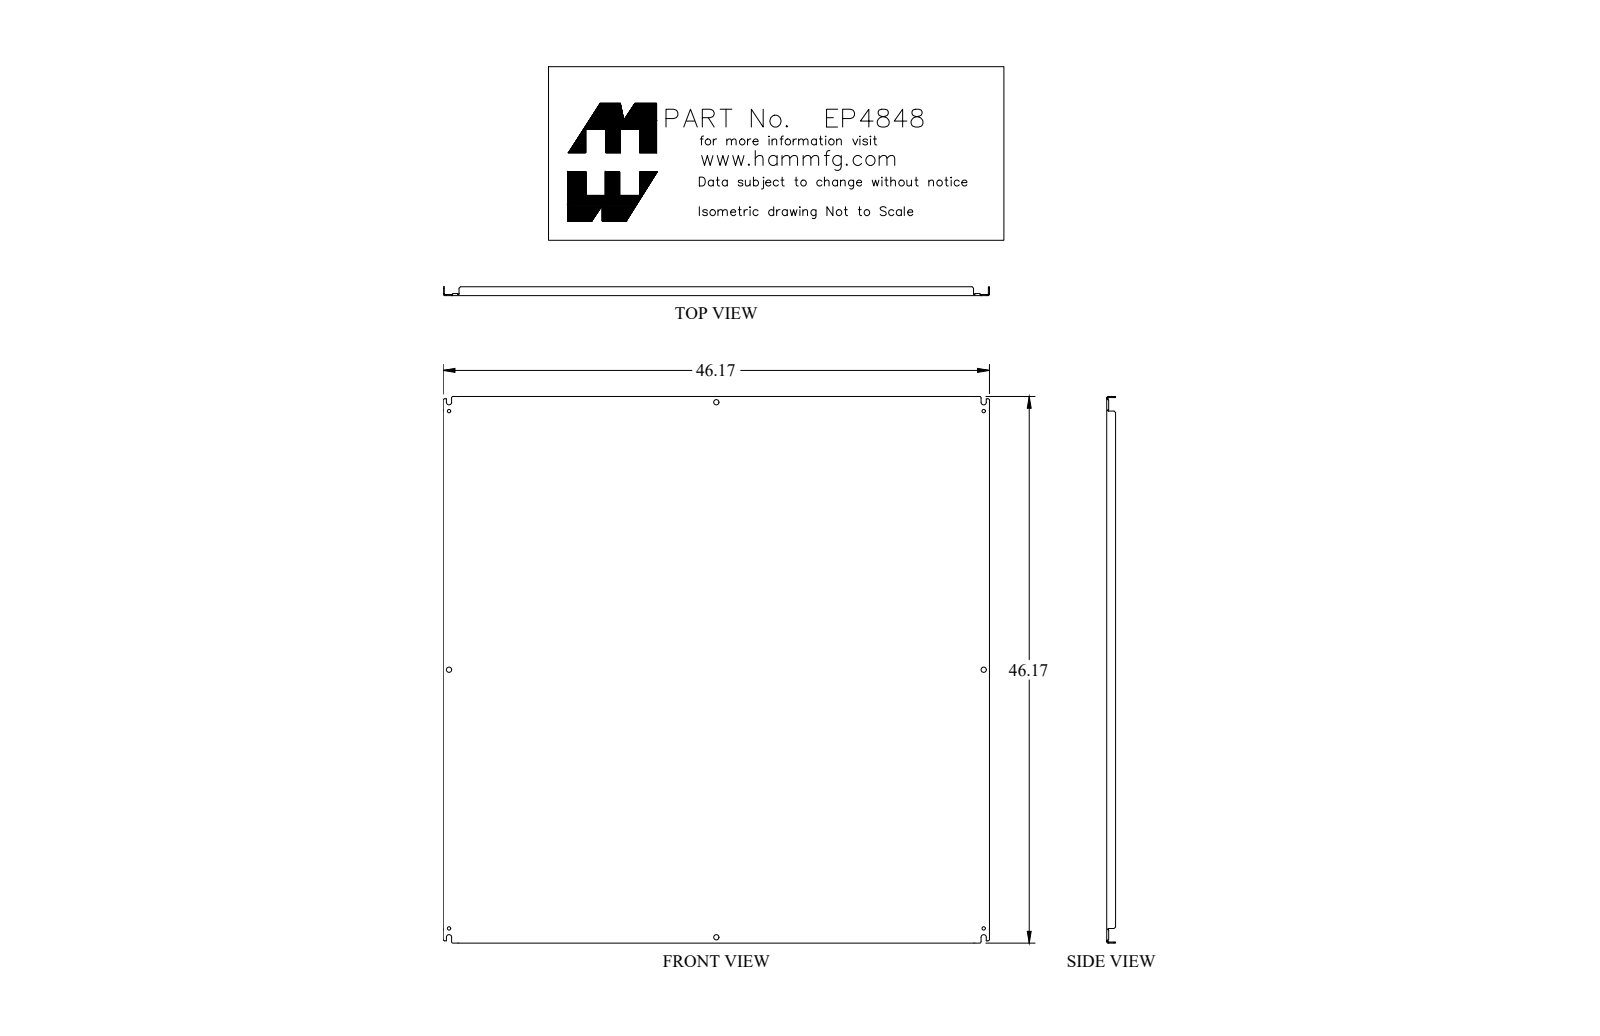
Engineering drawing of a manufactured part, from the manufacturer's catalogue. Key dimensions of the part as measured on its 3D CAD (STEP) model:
Part name (STEP PRODUCT): EP4848
STEP written by: SolidWorks 2018 (AUTOMOTIVE_DESIGN)
Units: inches
Bodies: 1 solid, 136 faces (74 planar, 46 cylindrical, 16 other)
Overall size (bounding box): 46.17 × 46.17 × 0.75
Volume: 212.5 in³ · Surface area: 4 492 in²
Round holes (diameter × count): ⌀0.281 ×4, ⌀0.437 ×4
Partial cylindrical surfaces — rounded edges, fillets, slot ends (radius × count): R0.048 ×4, R0.063 ×4, R0.143 ×4, R0.219 ×4
Main face-to-face distances: 0.095, 46.075, 45.98, 46.17, 0.75, 0.655, 0.171, 0.076, 0.579, 1.235
Hole centre spacings: 21.844, 22.607, 31.953, 45.188, 49.852, 50.191, 43.688, 62.854
